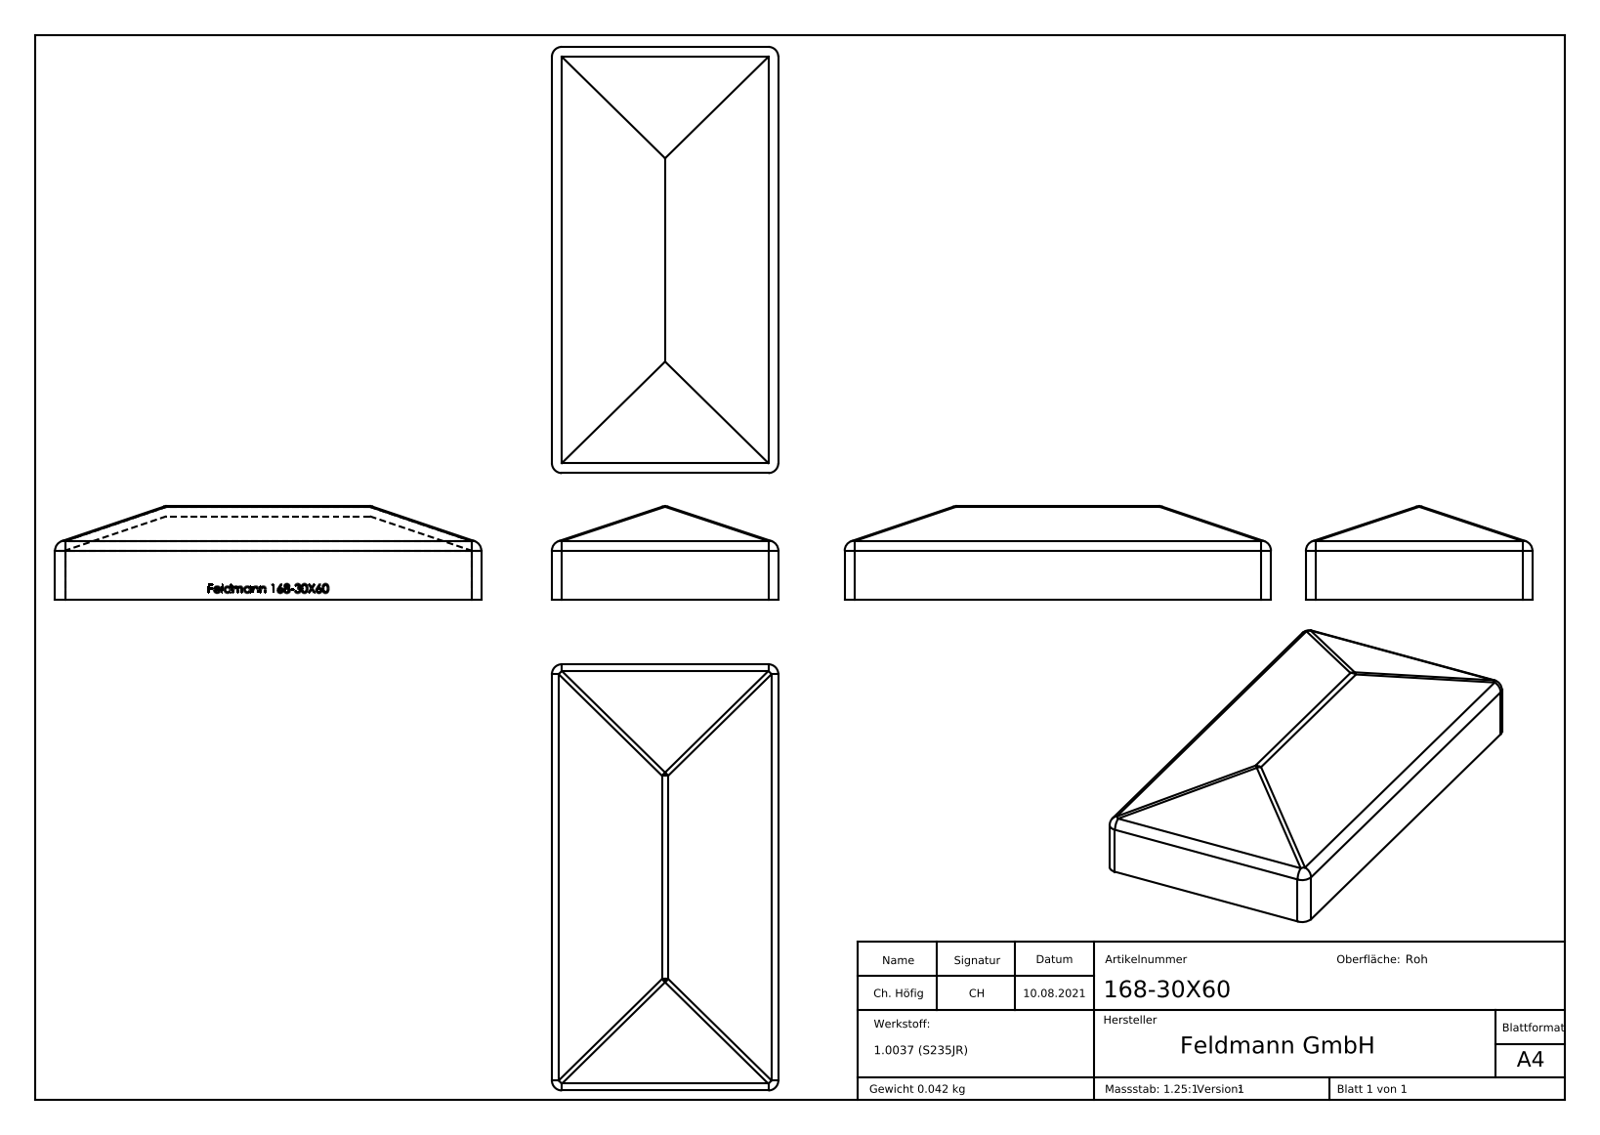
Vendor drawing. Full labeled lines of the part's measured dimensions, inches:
Part name (STEP PRODUCT): 168-30X60
STEP written by: SolidWorks 2018 (CONFIG_CONTROL_DESIGN)
Units: inches
Bodies: 1 solid, 263 faces (130 planar, 13 cylindrical, 120 other)
Overall size (bounding box): 2.52 × 1.339 × 0.551
Volume: 0.33 in³ · Surface area: 11.63 in²
Partial cylindrical surfaces — rounded edges, fillets, slot ends (radius × count): R0.059 ×13
Main face-to-face distances: 0.059, 1.28, 2.461, 1.339, 1.22, 2.402, 2.52, 0.055, 1.224, 1.283
